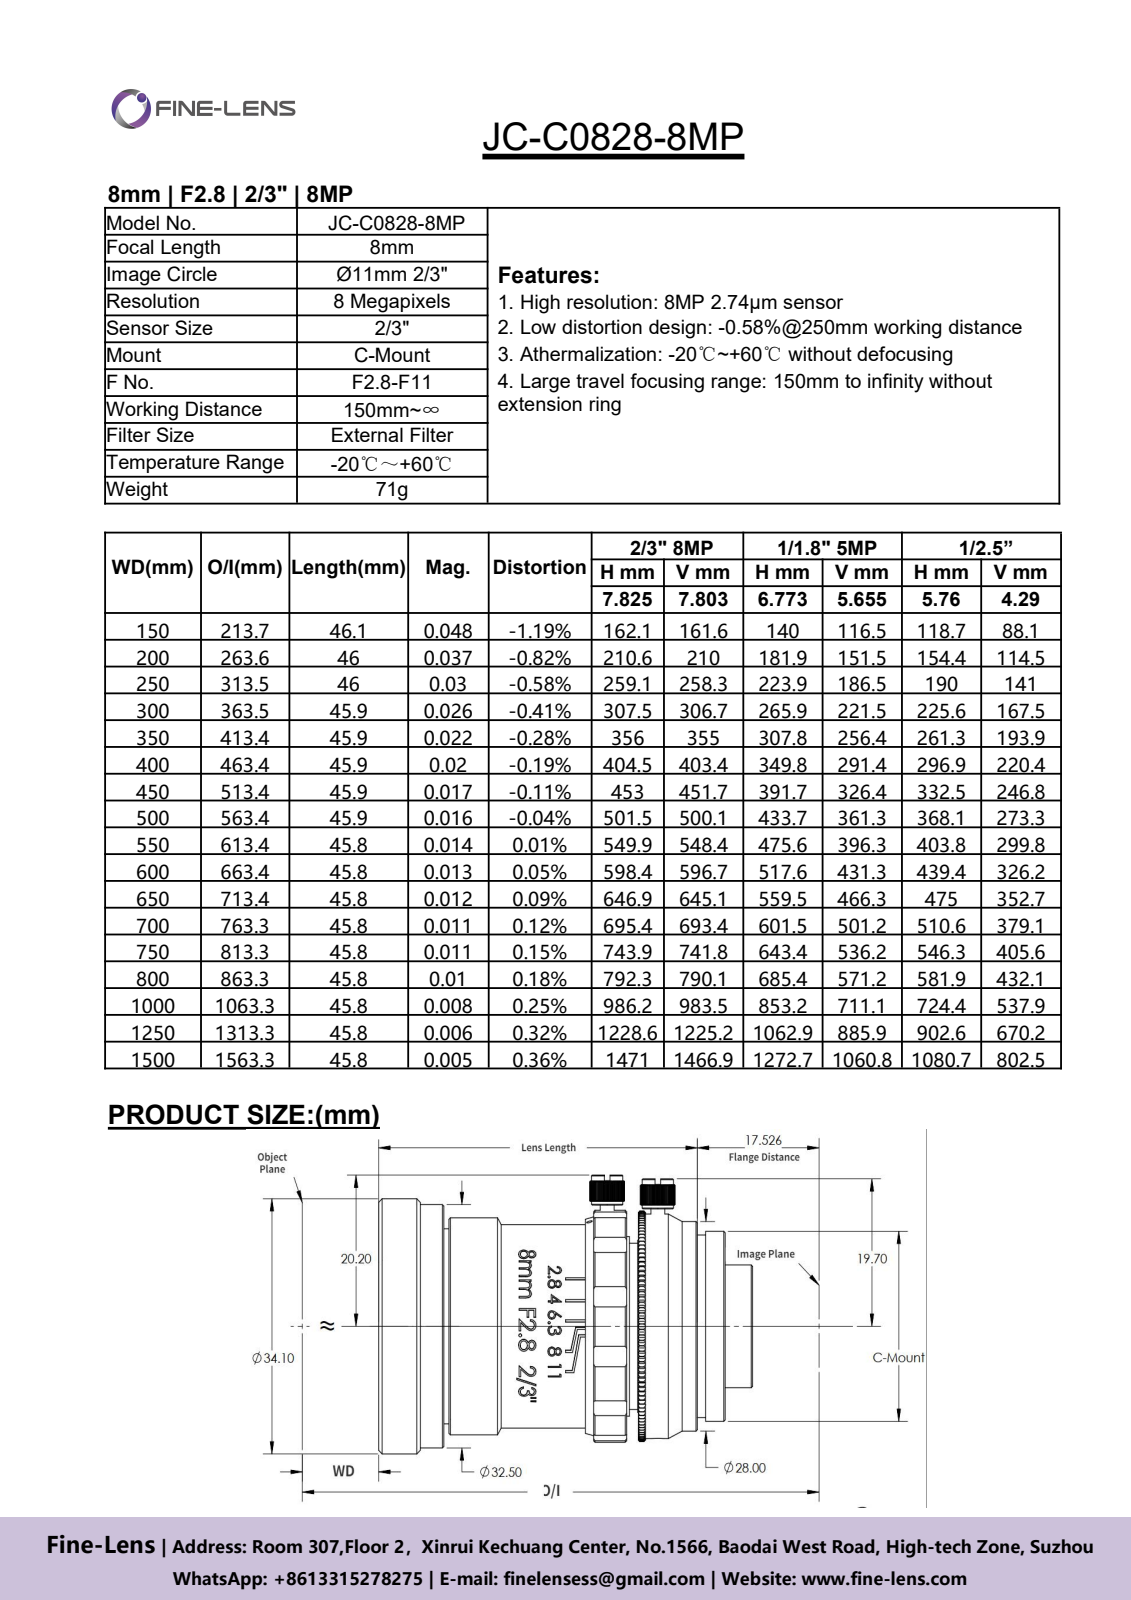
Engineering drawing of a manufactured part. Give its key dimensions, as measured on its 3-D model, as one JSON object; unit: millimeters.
{"part_name": "前镜筒", "step_written_by": "SolidWorks 2018 (CONFIG_CONTROL_DESIGN)", "units": "millimeters", "bodies": {"solids": 6, "faces": 1399, "planar": 477, "cylindrical": 320, "other": 602}, "overall_size": [52.63, 40.65, 34.1], "volume_mm3": 27083, "surface_area_mm2": 16697, "round_holes": [[1.6, 4], [0.8, 1], [2.8, 1], [10.6, 1], [12.2, 1], [20.5, 1], [20.9, 1], [22.4, 1], [24, 1], [24.2, 1], [26.25, 1], [27.6, 1]], "round_bosses_or_shafts": [[4.5, 2], [2, 2], [34.1, 1], [32.5, 1], [30.8, 1], [28, 1], [27.2, 1], [27, 1]], "partial_cylinders_radius": [[2.5, 14], [1, 1], [13.62, 1], [15.5, 1]], "face_to_face_distances": [9.33, 3.75, 37.66, 28.33, 4.5, 29.08, 33.91, 24.58, 4.83, 32.83]}
